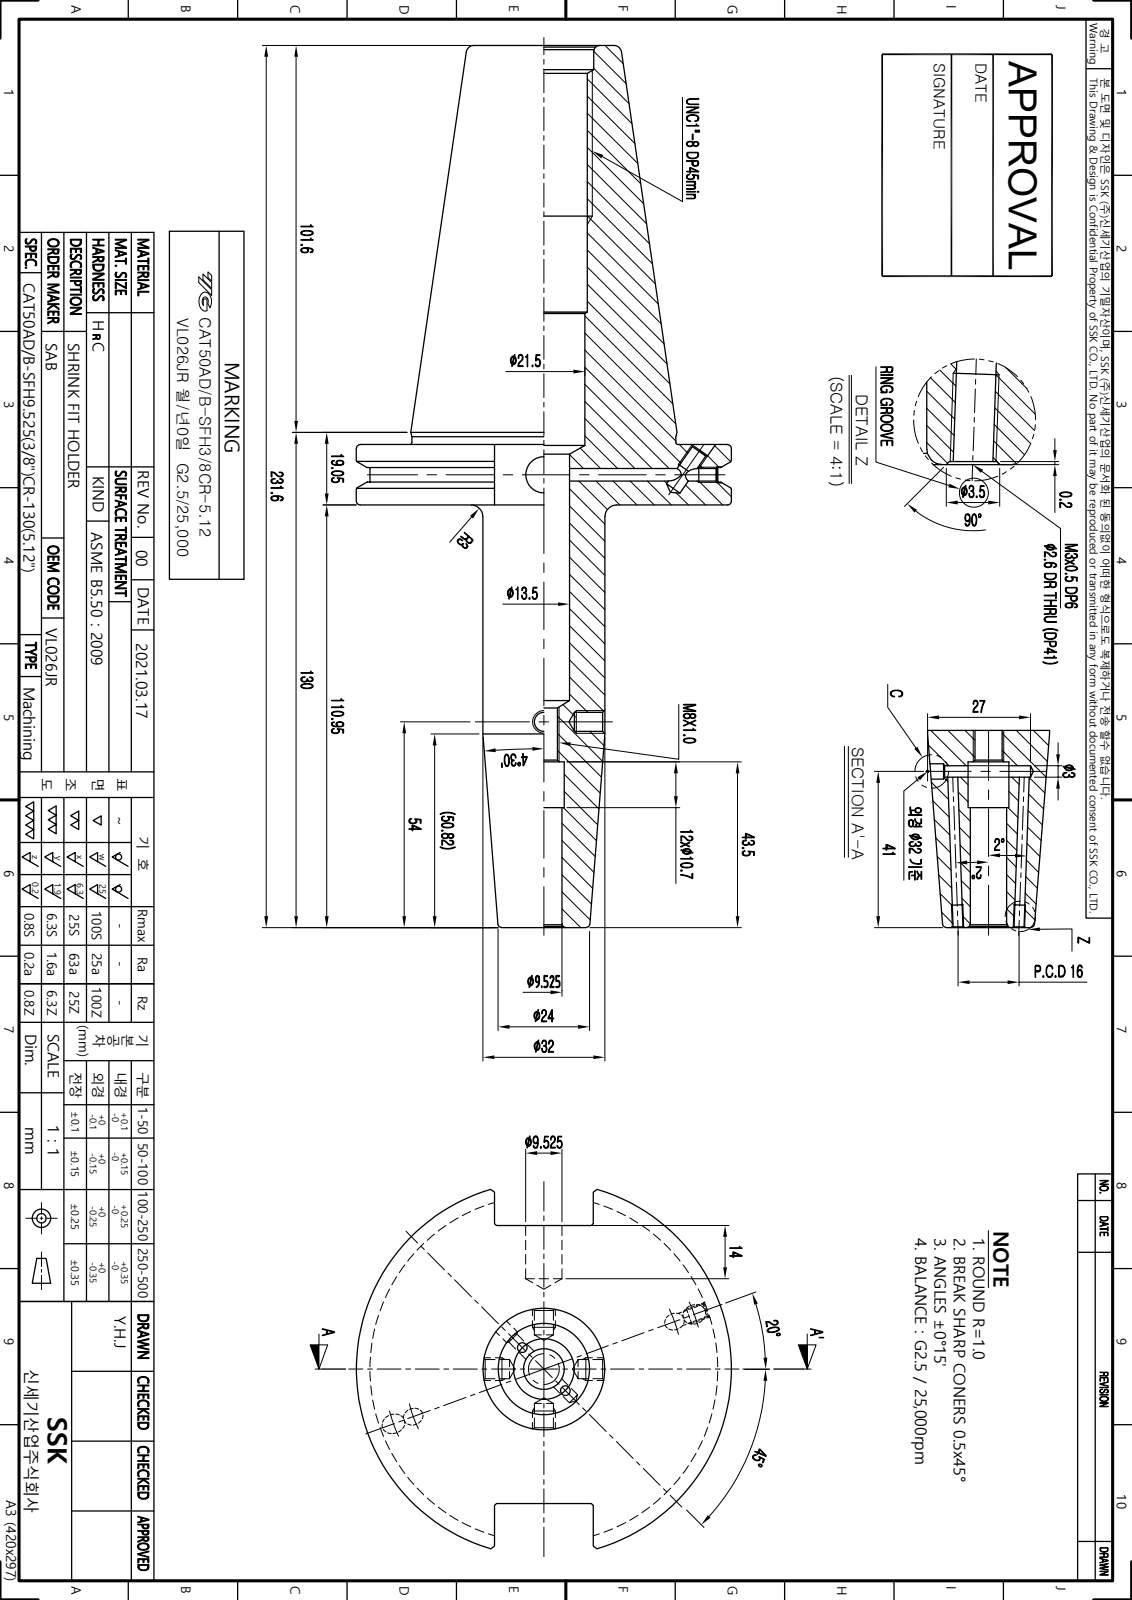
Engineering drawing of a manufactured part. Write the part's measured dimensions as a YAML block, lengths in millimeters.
part_name: "LO-CAT50ADB-SFH9.525CR-130"
step_written_by: "Autodesk Inventor 2022 (AUTOMOTIVE_DESIGN)"
units: millimeters
bodies: {solids: 1, faces: 95, planar: 37, cylindrical: 33, other: 25}
overall_size: [231.6, 98.42, 94.69]
volume: 389968
surface_area: 59542
round_holes:
  - {diameter: 2.46, count: 2}
  - {diameter: 3.24, count: 2}
  - {diameter: 4.13, count: 2}
  - {diameter: 4.2, count: 2}
  - {diameter: 5, count: 2}
  - {diameter: 9.53, count: 2}
  - {diameter: 3, count: 1}
  - {diameter: 4, count: 1}
  - {diameter: 6.92, count: 1}
  - {diameter: 10.7, count: 1}
  - {diameter: 13.5, count: 1}
  - {diameter: 21.5, count: 1}
round_bosses_or_shafts:
  - {diameter: 98.42, count: 1}
  - {diameter: 91.29, count: 1}
  - {diameter: 69.25, count: 1}
  - {diameter: 32, count: 1}
face_to_face_distances: [15.88, 104.77, 120.65, 73.03, 25.9, 231.6, 126.83, 110.95, 110.82, 6.05]
